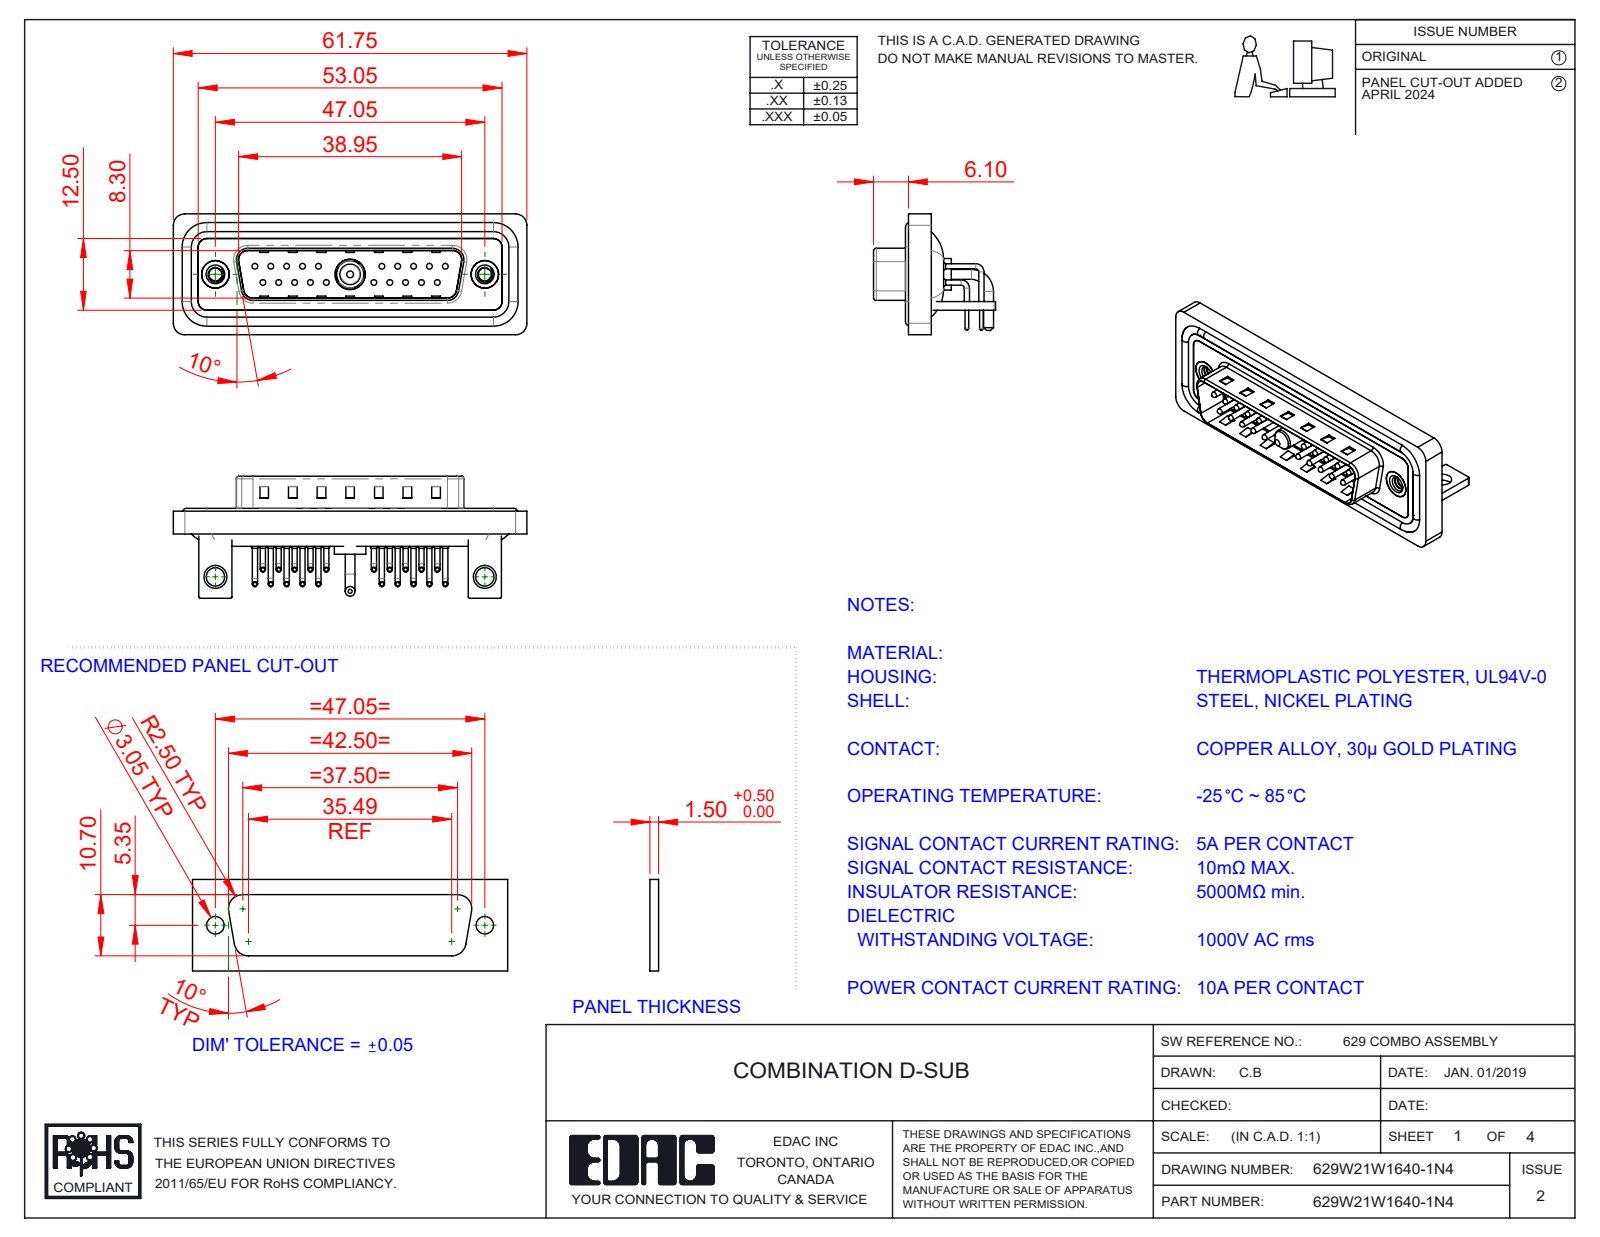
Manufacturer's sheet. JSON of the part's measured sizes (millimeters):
{"part_name": "629Combo Shell Front_25 Contacts; 629Combo Shell Rear_25 Contacts; 629W21W1640-1N4; Power Pin_10A RA (+6 more)", "step_written_by": "SolidWorks 2023 (CONFIG_CONTROL_DESIGN)", "units": "millimeters", "bodies": {"solids": 31, "faces": 2766, "planar": 1519, "cylindrical": 947, "other": 300}, "overall_size": [61.75, 21.3, 21.1], "volume_mm3": 7637, "surface_area_mm2": 13257, "round_holes": [[0.75, 20], [1.6, 20], [2, 20], [2.26, 2], [3.2, 2], [4, 2], [4.8, 2], [5, 2], [4.85, 1], [5.3, 1]], "round_bosses_or_shafts": [[0.9, 40], [1.5, 20], [1, 20], [0.65, 20], [1.6, 4], [4.9, 2], [1.7, 2], [5.5, 1]], "partial_cylinders_radius": [[1.01, 20], [2, 19], [1.5, 18], [0.25, 16], [0.5, 9], [1.6, 8], [0.6, 4], [0.65, 4]], "face_to_face_distances": [0.4, 0.8, 2.1, 2.9, 1.5, 1.1, 4.1, 1.6, 4.5, 3.7], "hole_center_spacings": [3.16, 2.77, 5.54, 8.31, 5.04, 19.39, 20.97, 22.16]}
